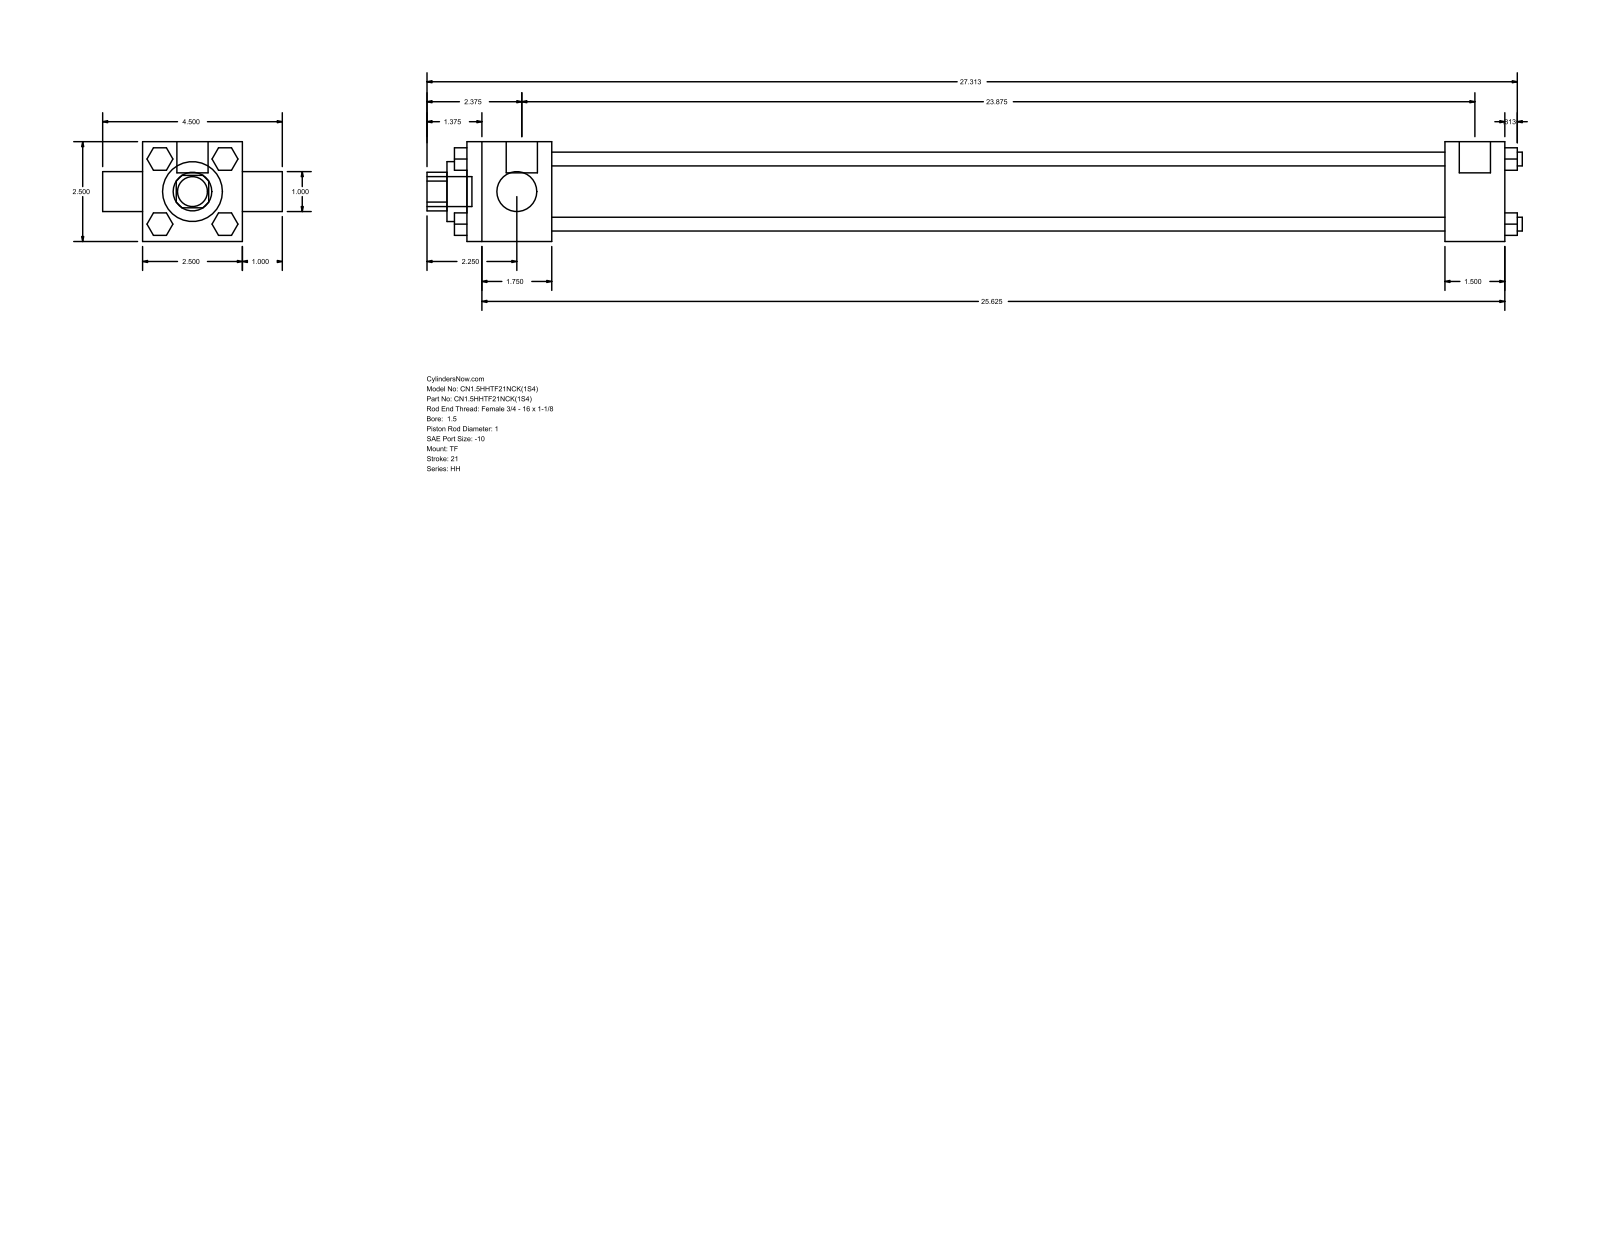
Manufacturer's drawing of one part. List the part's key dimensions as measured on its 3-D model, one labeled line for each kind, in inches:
Part name (STEP PRODUCT): HH_TF__0150_1
STEP written by: GSSL Pune (CONFIG_CONTROL_DESIGN)
Units: inches
Bodies: 0 solids, 120 faces (92 planar, 28 cylindrical, 0 other)
Overall size (bounding box): 27.437 × 4.5 × 2.5
Round holes (diameter × count): ⌀1 ×2, ⌀1.5 ×1, ⌀1.75 ×1
Round bosses / shafts (diameter × count): ⌀0.345 ×4, ⌀0.219 ×3, ⌀0.781 ×2, ⌀0.75 ×1
Partial cylindrical surfaces — rounded edges, fillets, slot ends (radius × count): R0.484 ×1
Main face-to-face distances: 2.5, 23.875, 22.375, 1.5, 2.125, 24.5, 26, 26.313, 1, 0.815
